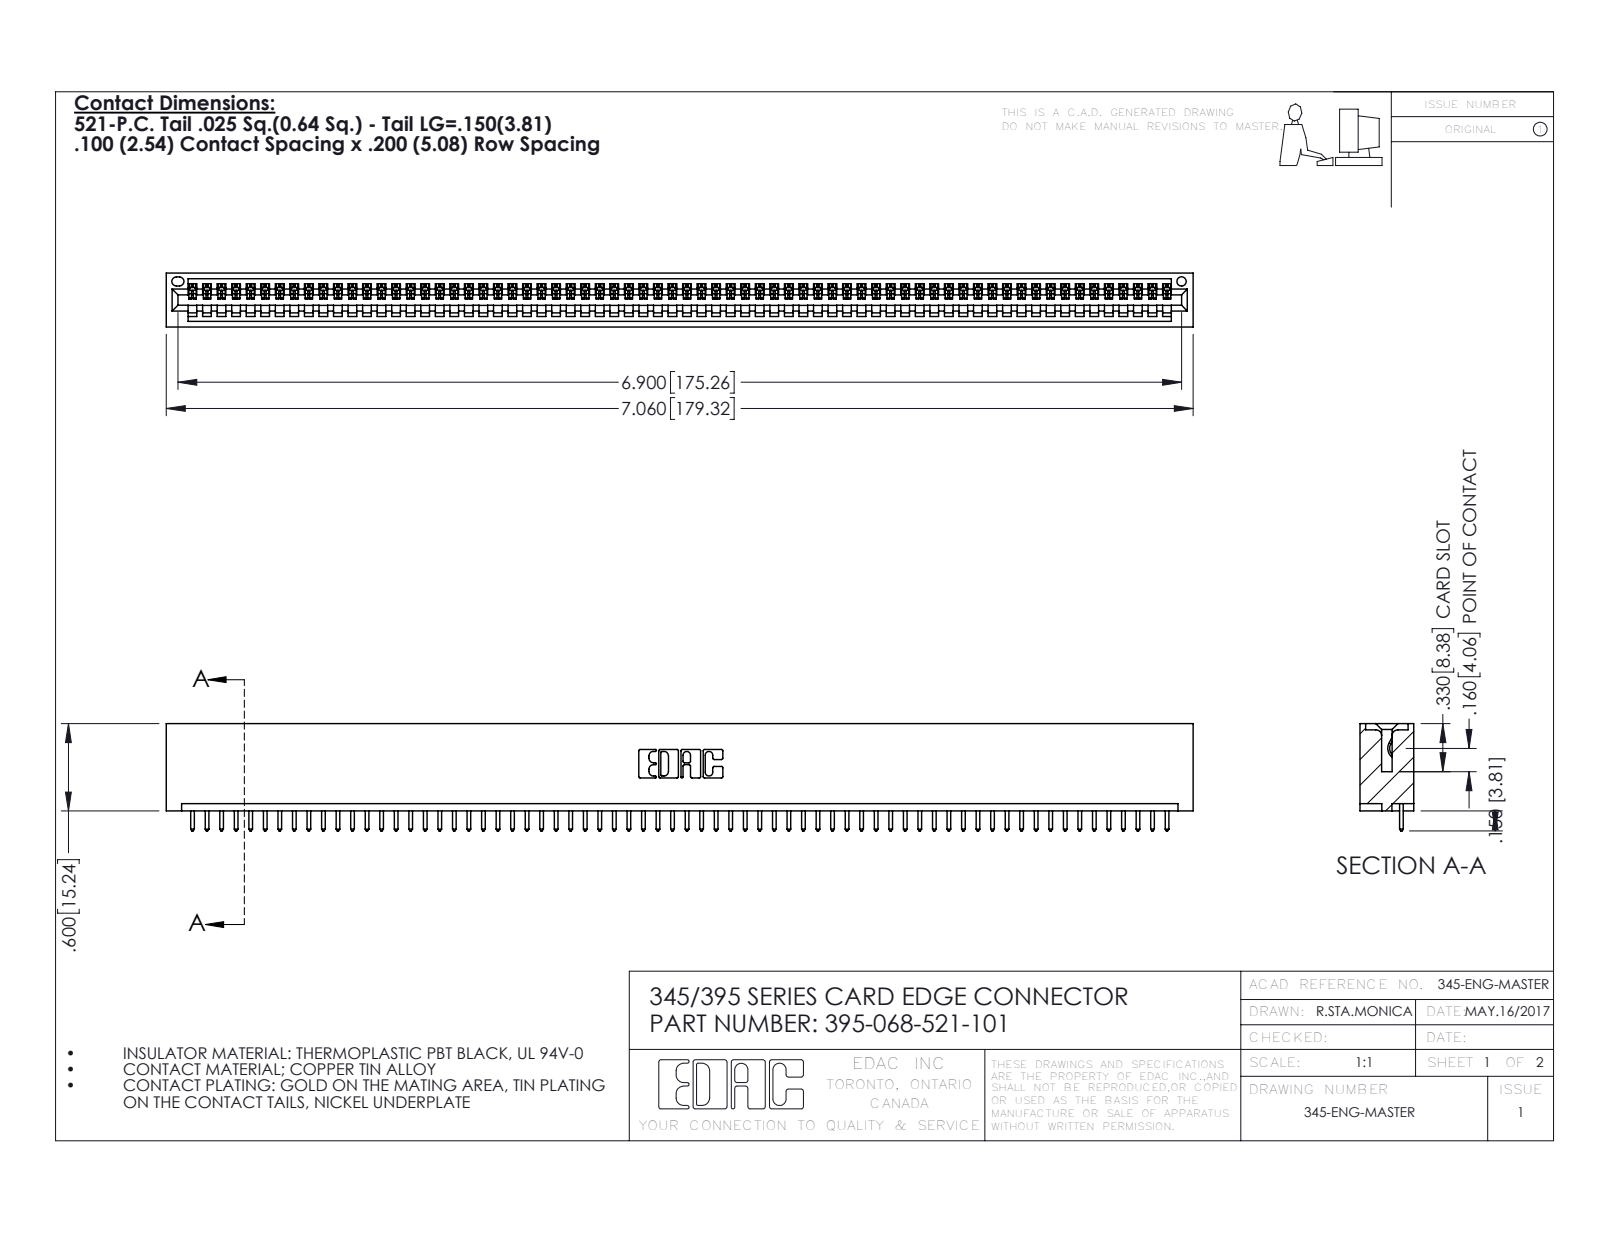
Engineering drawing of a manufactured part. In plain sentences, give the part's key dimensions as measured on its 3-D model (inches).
The part is named "345 Part_No Mounting Lugs; 395-068-521-101; 345-292-001_345-293-121". Its 3-D file was written by "SolidWorks 2016 (CONFIG_CONTROL_DESIGN)". It is 69 solids with 4062 faces: 2796 planar, 1266 cylindrical and 0 other. Overall it measures 7.06 by 0.737 by 0.37 inches. Its volume is 1.076 cubic inches and its surface area 36 square inches. Round holes: 1 of diameter 0.064. Partial cylindrical surfaces (rounded edges, fillets, slot ends): 136 of radius 0.006, 136 of radius 0.01, 22 of radius 0.01, 6 of radius 0.007, 6 of radius 0.031, 3 of radius 0.026, 2 of radius 0.031, 2 of radius 0.04. The main face-to-face distances are 0.298, 0.072, 0.37, 0.2, 0.098, 0.272, 0.025, 0.225, 0.149, 0.072.
